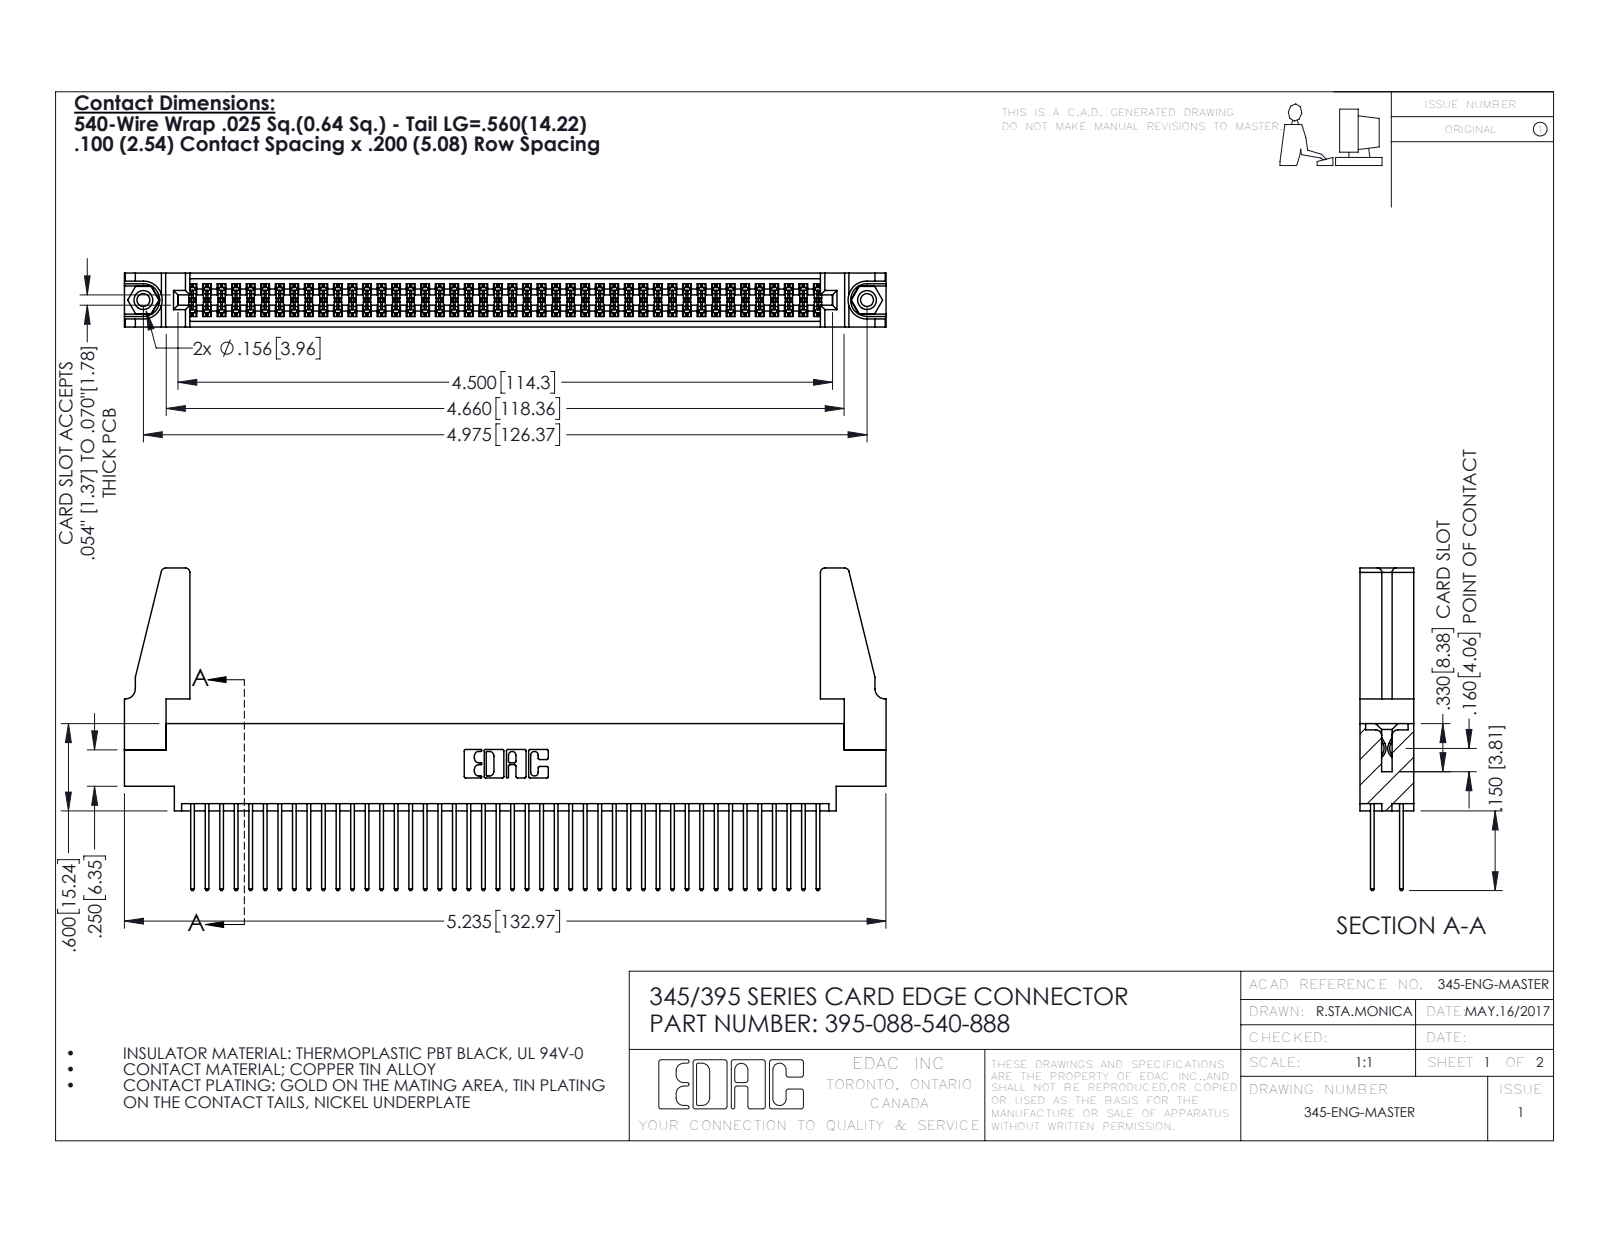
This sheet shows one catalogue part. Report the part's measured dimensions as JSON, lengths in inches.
{"part_name": "345-292-001_345-293-140; 395-088-540-888; 345 Part_0.170 Offset - 0.156 Dia-TH; 345-220-078_345-220-088 (+1 more)", "step_written_by": "SolidWorks 2016 (CONFIG_CONTROL_DESIGN)", "units": "inches", "bodies": {"solids": 93, "faces": 4654, "planar": 3060, "cylindrical": 1578, "other": 16}, "overall_size": [5.236, 2.217, 0.37], "volume_in3": 1.001, "surface_area_in2": 37.67, "round_holes": [[0.089, 2], [0.125, 2], [0.156, 2], [0.064, 1]], "round_bosses_or_shafts": [[0.155, 2]], "partial_cylinders_radius": [[0.006, 132], [0.01, 88], [0.01, 22], [0.03, 8], [0.007, 6], [0.031, 6], [0.026, 3], [0.014, 2]], "face_to_face_distances": [0.072, 0.298, 0.37, 0.2, 0.098, 0.272, 0.025, 0.225, 0.175, 0.149], "hole_center_spacings": [0.27, 4.739, 4.975]}
